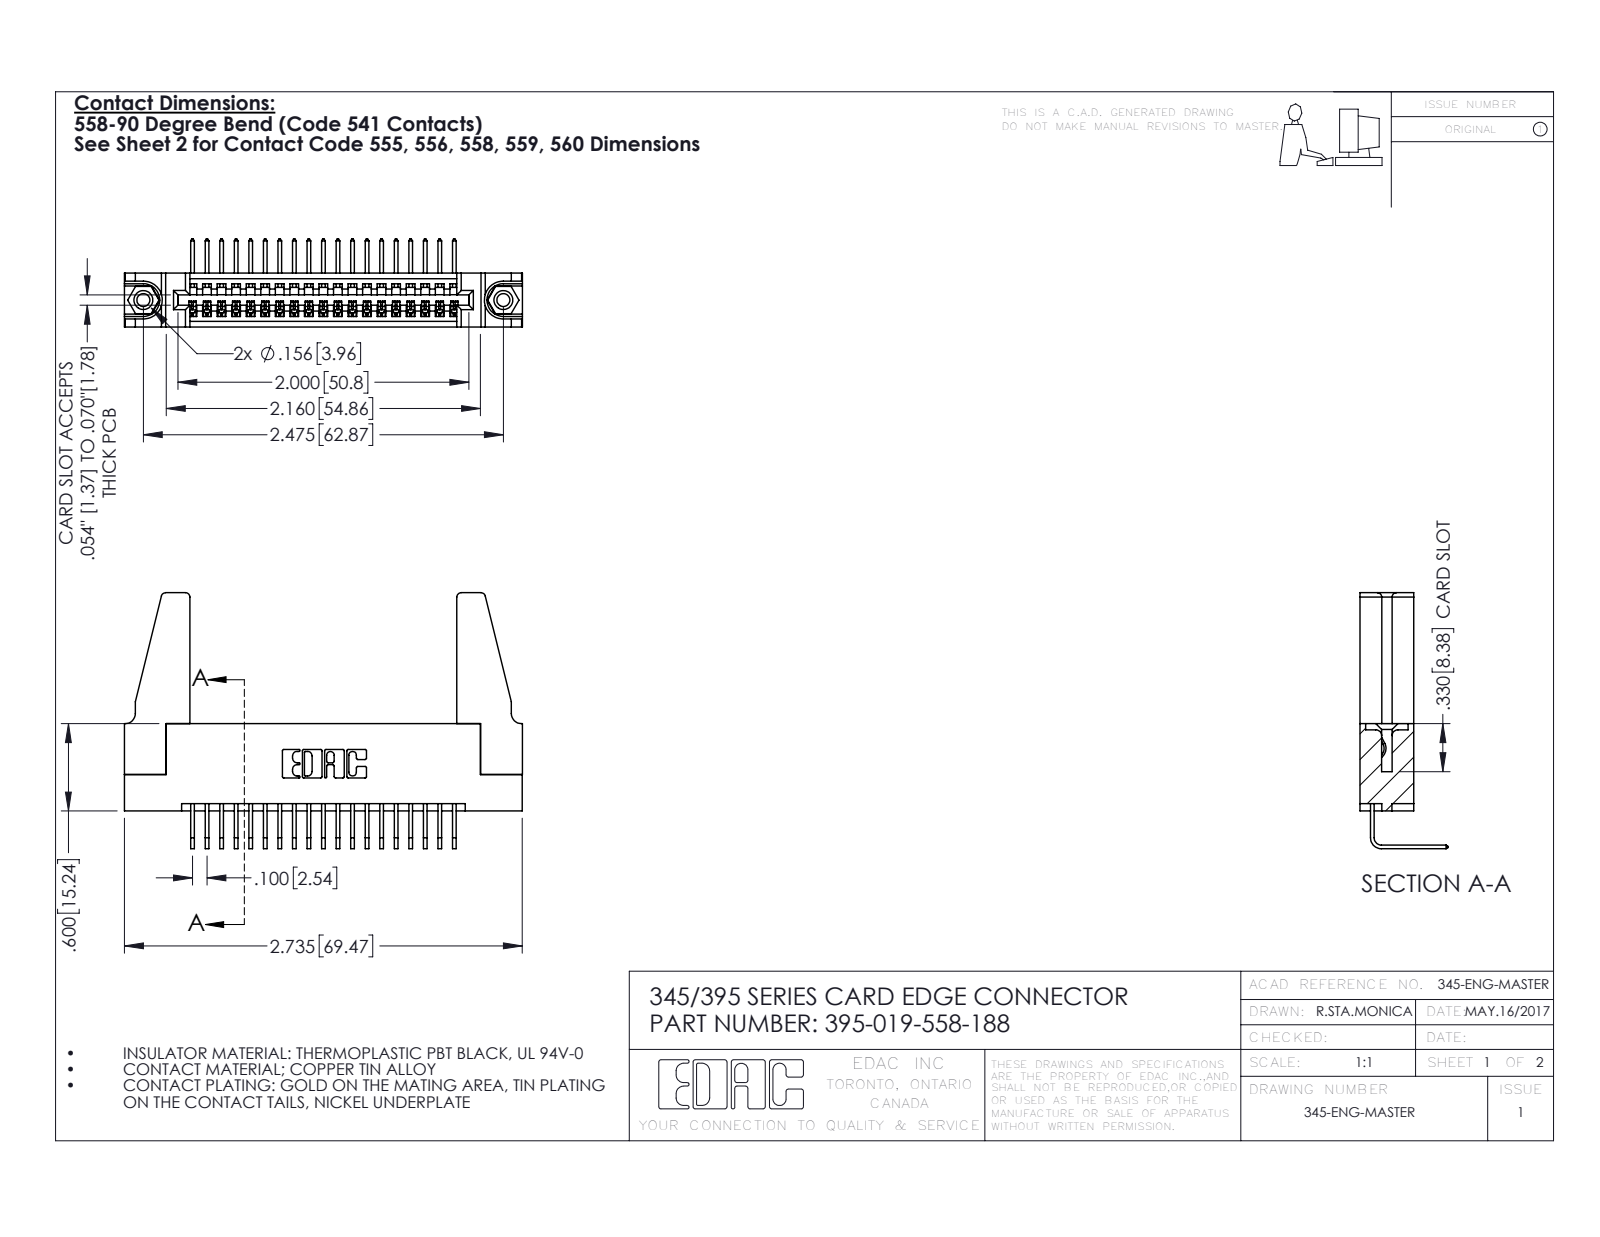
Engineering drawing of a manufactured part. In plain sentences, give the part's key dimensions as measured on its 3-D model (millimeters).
The part is named "345-292-001_558 Tail - 2; 345 Part_Flush Mounting Lugs - 0.156 Dia-TH; 345-250-001_345-250-001-102; 395-019-558-188 (+1 more)". Its 3-D file was written by "SolidWorks 2016 (CONFIG_CONTROL_DESIGN)". It is 24 solids with 1390 faces: 950 planar, 424 cylindrical and 16 other. Overall it measures 69.5 by 44.7 by 15.4 millimeters. Its volume is 9 730 cubic millimeters and its surface area 11 790 square millimeters. Round holes: 2 of diameter 2.3, 2 of diameter 3.2, 2 of diameter 4, 1 of diameter 1.6. Round bosses or shafts: 2 of diameter 3.9. Partial cylindrical surfaces (rounded edges, fillets, slot ends): 38 of radius 0.2, 22 of radius 0.3, 8 of radius 0.8, 6 of radius 0.2, 6 of radius 0.8, 3 of radius 0.7, 2 of radius 0.8, 2 of radius 1. The main face-to-face distances are 9.4, 1.8, 7.6, 5.1, 2.5, 6.9, 0.6, 5.7, 3.8, 3.8. The hole center spacings are 6.9, 56.9, 62.9.
